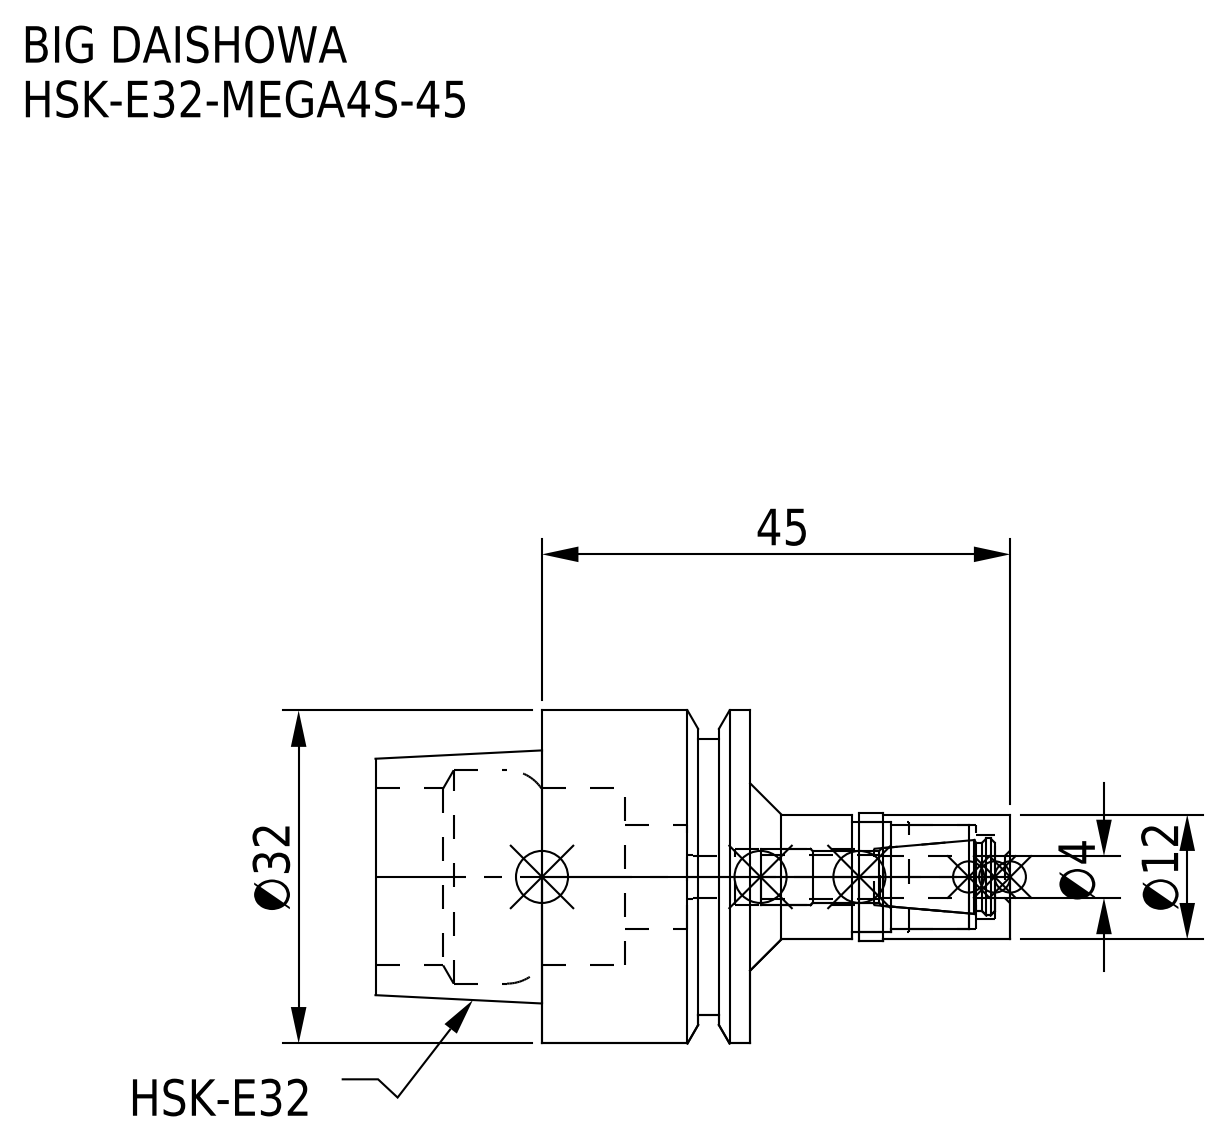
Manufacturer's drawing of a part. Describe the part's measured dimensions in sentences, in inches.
The part is named "DXF_TEMP_ASSY_ASM_4_ASM.stp; HE32MS04045-040_ASM.stp; HSK-E32-MEGA4S-45-040.stp; HSK-E32-MEGA4S-45 (+3 more)". Its 3-D file was written by "SolidWorks 2019 (CONFIG_CONTROL_DESIGN)". It is 2 solids with 74 faces: 18 planar, 40 cylindrical and 16 other. Overall it measures 2.402 by 1.26 by 1.26 inches. Its volume is 1.088 cubic inches and its surface area 13.93 square inches. Round holes: 1 of diameter 0.161, 1 of diameter 0.165, 1 of diameter 0.213, 1 of diameter 0.315, 1 of diameter 0.394, 1 of diameter 0.413, 1 of diameter 0.669, 1 of diameter 0.807. Round bosses or shafts: 1 of diameter 1.26, 1 of diameter 1.043, 1 of diameter 0.484, 1 of diameter 0.472. The main face-to-face distances are 0.787, 0.63, 1.417, 0.474, 0.313, 0.943, 0.984, 0.118, 0.591, 1.459.
